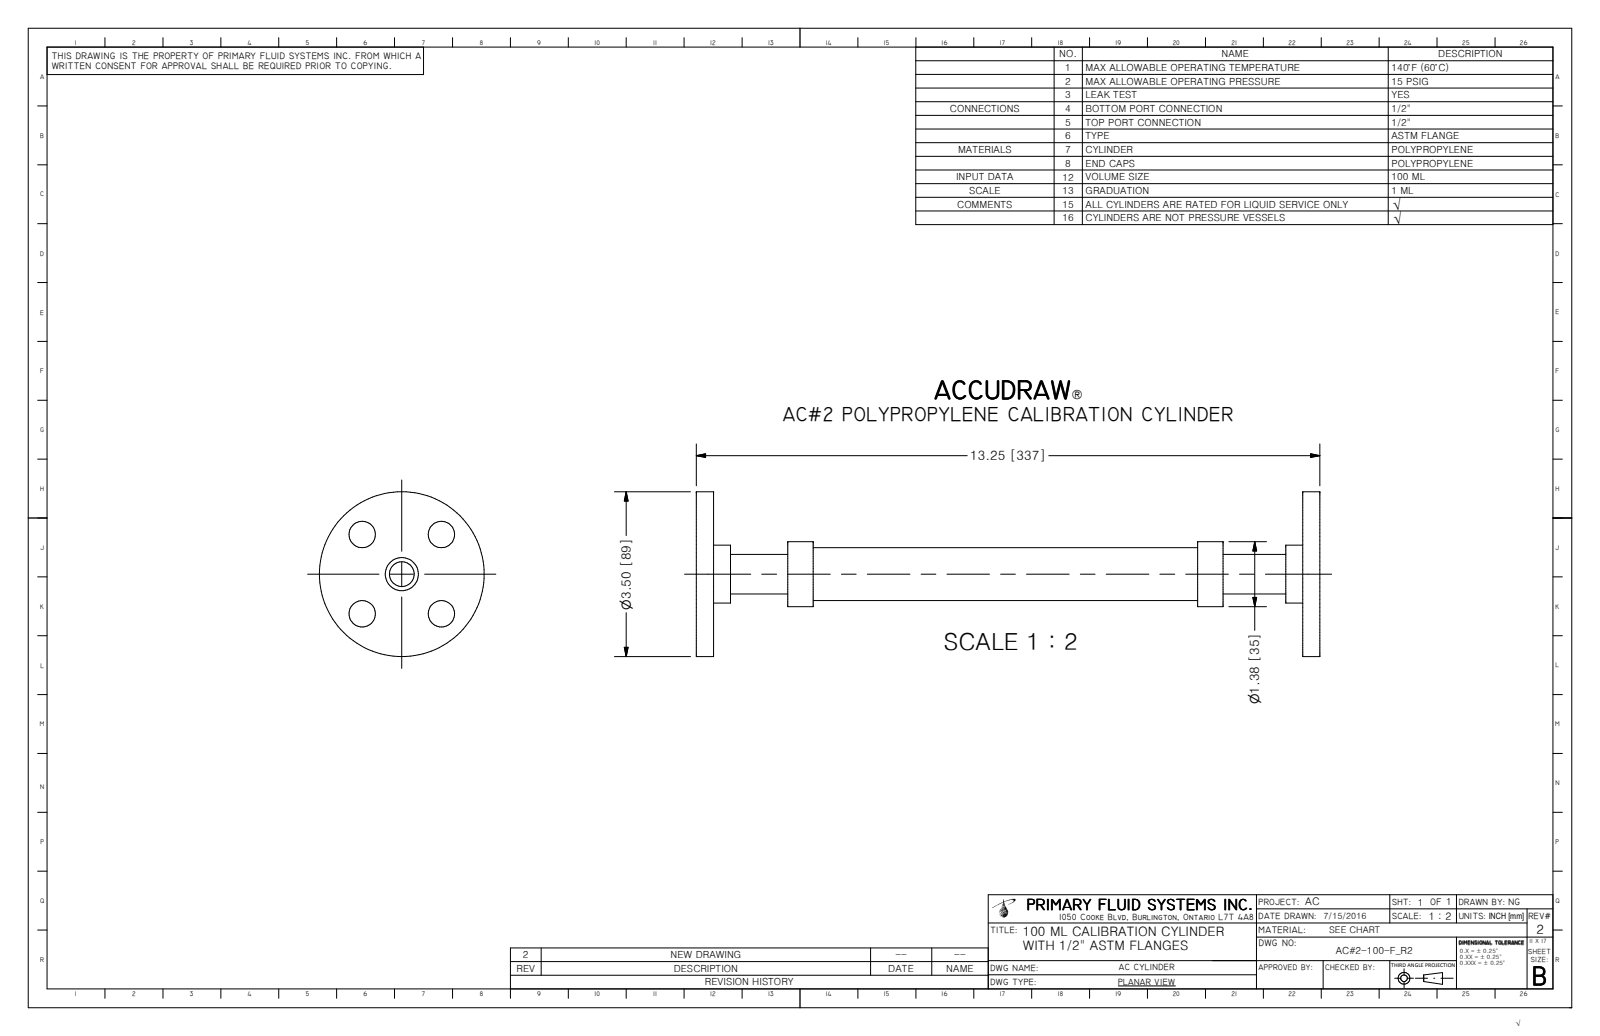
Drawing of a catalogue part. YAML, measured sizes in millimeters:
part_name: "AC#2-100-F_R2; SA-50FLG-PP_R0; FLG-50PP_R0; PIPE-50PP-SCH80 (+3 more)"
step_written_by: "Autodesk Inventor 2009 (AUTOMOTIVE_DESIGN)"
units: millimeters
bodies: {solids: 7, faces: 52, planar: 22, cylindrical: 28, other: 2}
overall_size: [336.6, 88.9, 88.9]
volume: 179600
surface_area: 93230
round_holes:
  - {diameter: 14.2, count: 4}
  - {diameter: 13.4, count: 1}
  - {diameter: 17.5, count: 1}
  - {diameter: 17.9, count: 1}
  - {diameter: 21.3, count: 1}
  - {diameter: 25.5, count: 1}
round_bosses_or_shafts:
  - {diameter: 88.9, count: 1}
  - {diameter: 35.1, count: 1}
  - {diameter: 31.2, count: 1}
  - {diameter: 28.6, count: 1}
  - {diameter: 27.6, count: 1}
  - {diameter: 25.7, count: 1}
face_to_face_distances: [9.3, 327.3, 336.6, 318, 19.1, 215.9, 49.4, 284.3, 40.1, 275]
hole_center_spacings: [30.2, 42.7, 60.5]
